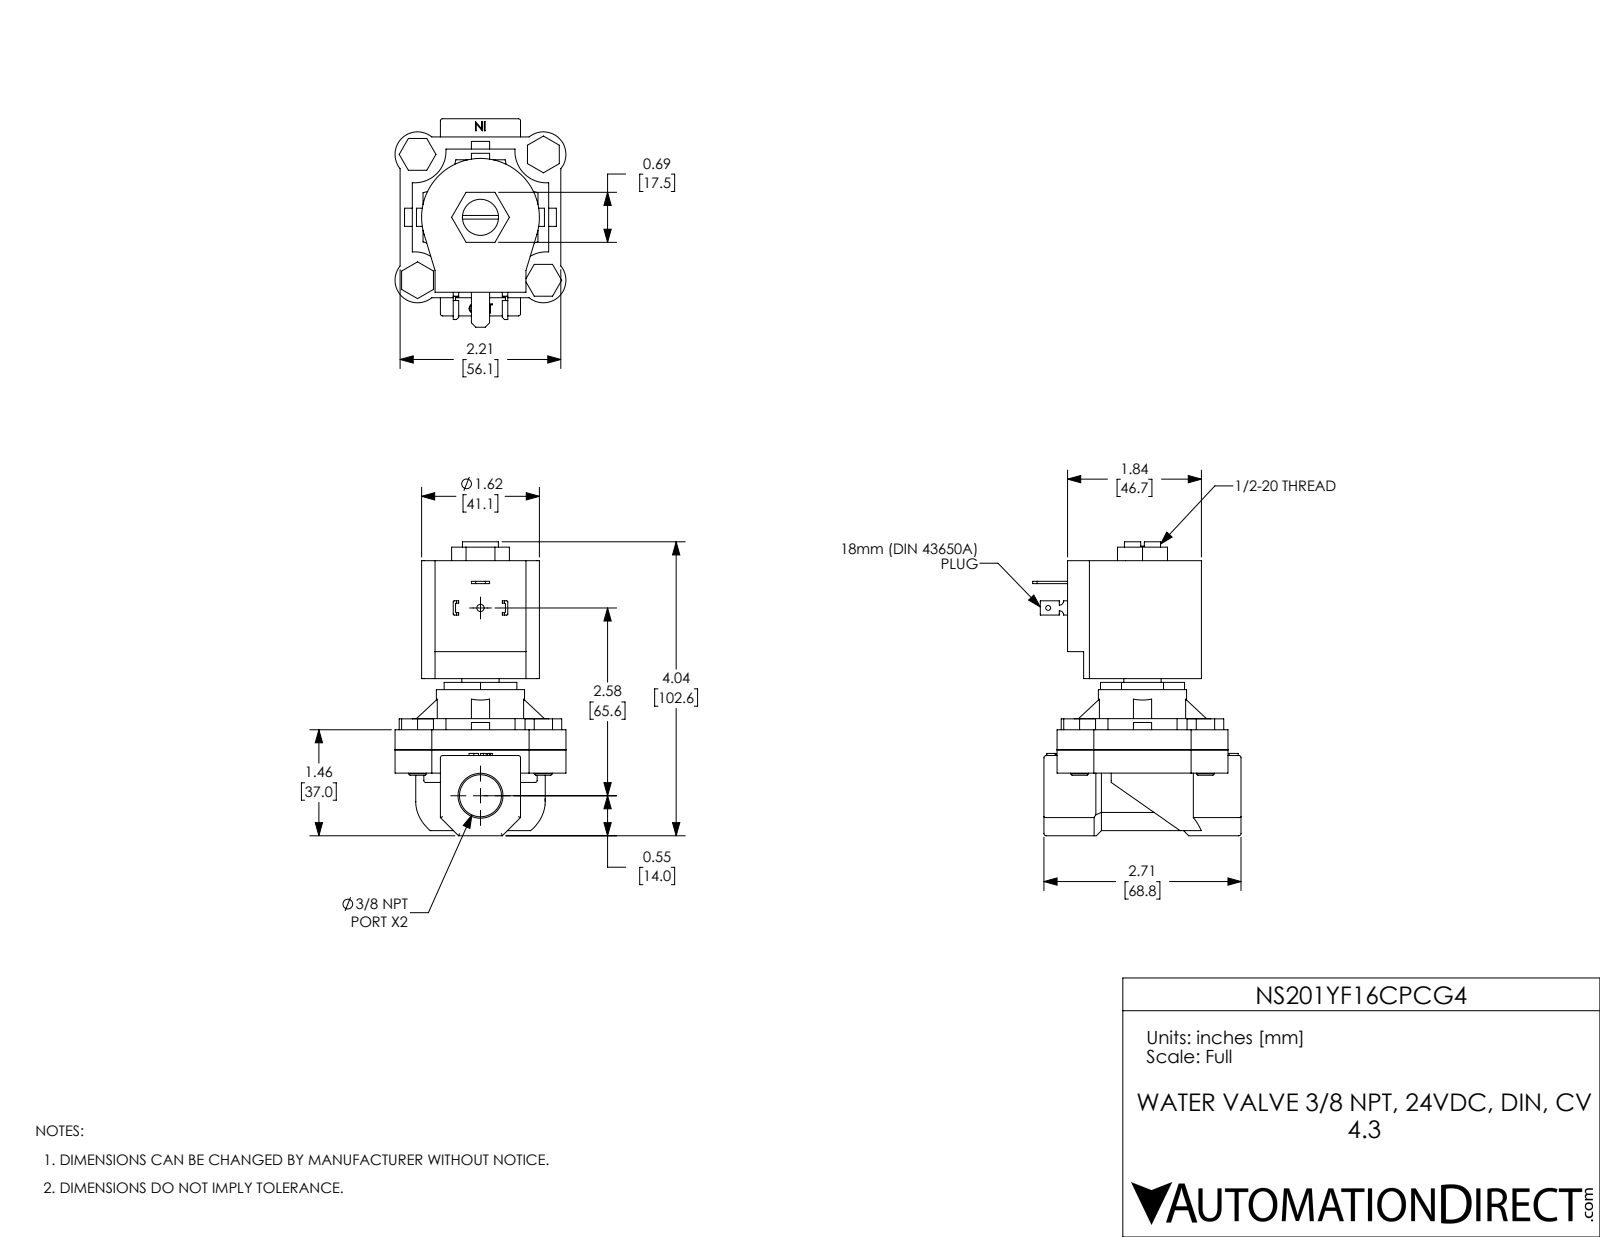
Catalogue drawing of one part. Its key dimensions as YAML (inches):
part_name: "NS201YF16CPCG4"
step_written_by: "SolidWorks 2021 (CONFIG_CONTROL_DESIGN)"
units: inches
bodies: {solids: 11, faces: 383, planar: 237, cylindrical: 113, other: 33}
overall_size: [4.04, 2.865, 2.35]
volume: 10.3
surface_area: 66.77
round_holes:
  - {diameter: 0.25, count: 4}
  - {diameter: 0.067, count: 1}
  - {diameter: 0.1, count: 1}
  - {diameter: 0.496, count: 1}
  - {diameter: 0.512, count: 1}
  - {diameter: 0.578, count: 1}
  - {diameter: 1.155, count: 1}
round_bosses_or_shafts:
  - {diameter: 0.248, count: 4}
  - {diameter: 1.213, count: 1}
partial_cylinders:
  - {radius: 0.03, count: 15}
  - {radius: 0.015, count: 8}
  - {radius: 0.31, count: 4}
  - {radius: 0.432, count: 4}
  - {radius: 0.579, count: 4}
  - {radius: 0.06, count: 2}
  - {radius: 0.81, count: 1}
  - {radius: 0.89, count: 1}
face_to_face_distances: [0.276, 2.599, 2.323, 0.32, 0.596, 2.919, 0.554, 1.656, 0.25, 2.46]
hole_center_spacings: [1.223, 1.73, 2.446, 2.581]
